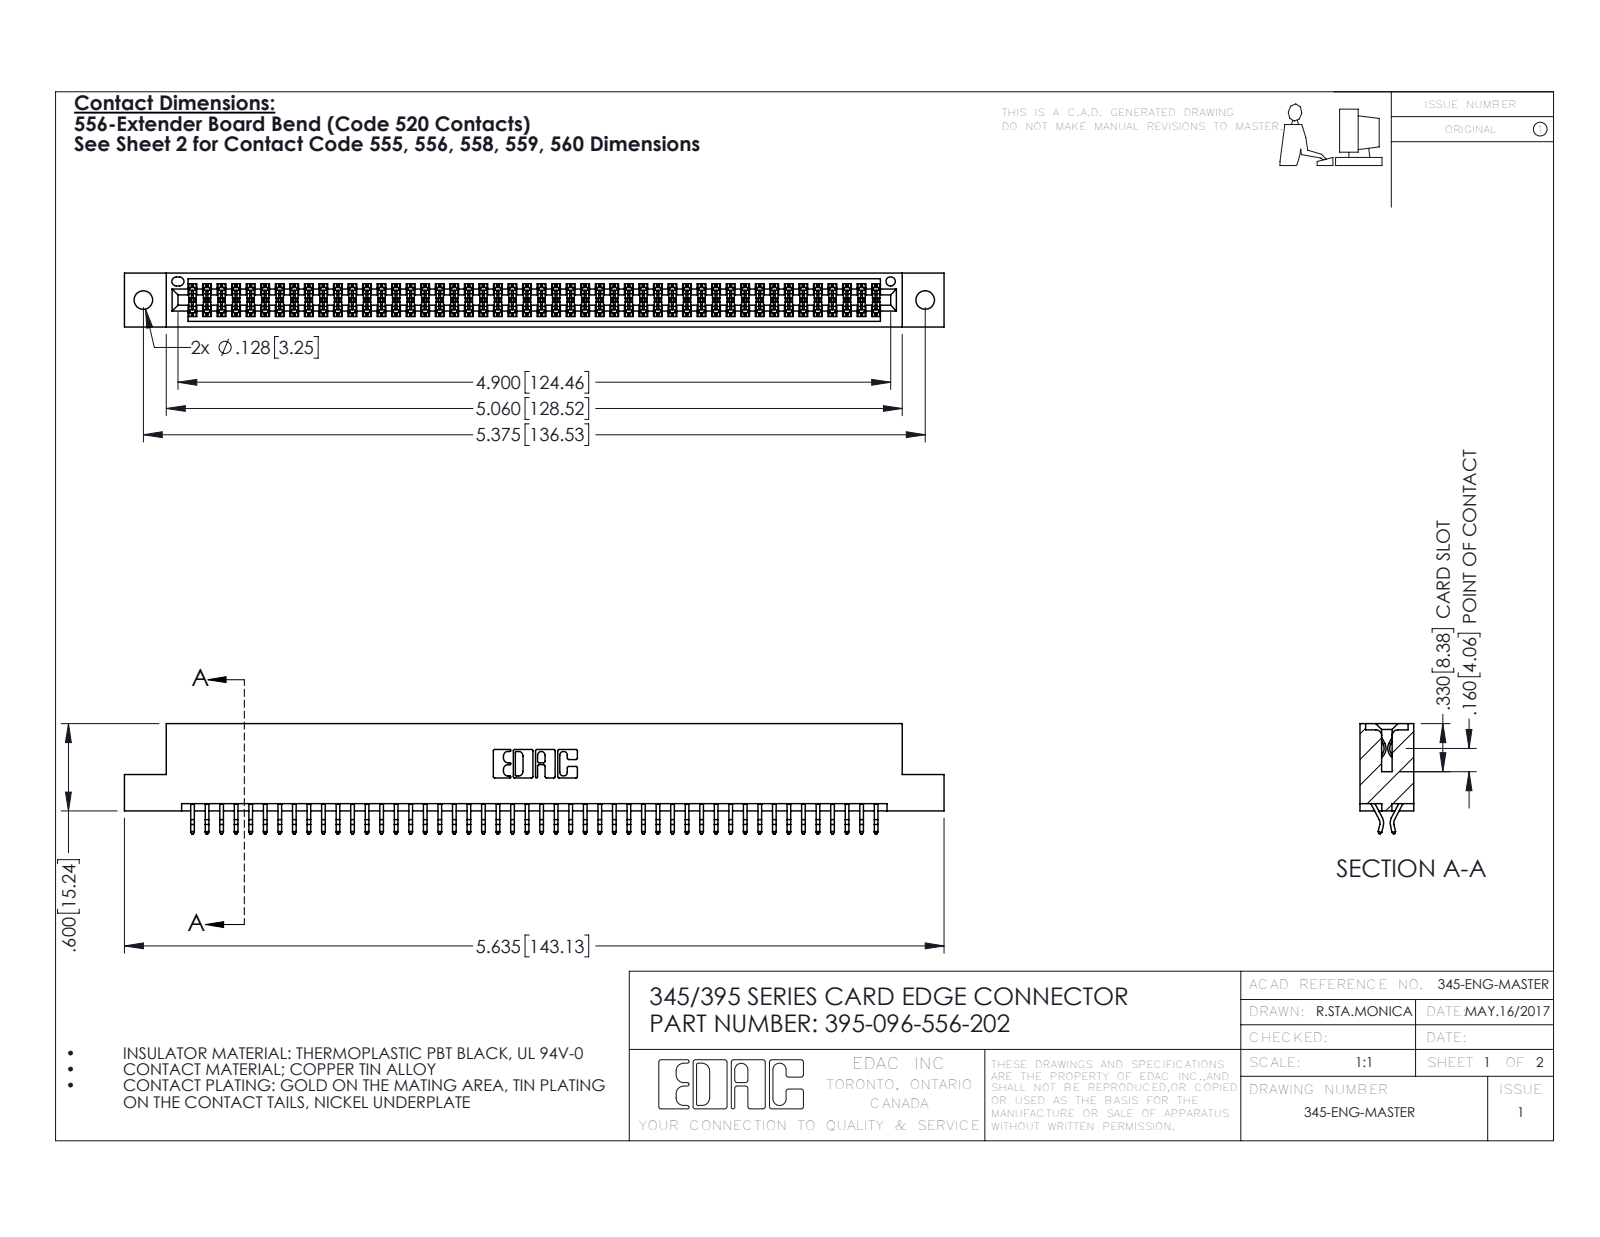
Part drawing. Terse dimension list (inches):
name: 395-096-556-202; 345-292-001_556 Tail; 345 Part_Flush Mounting Lugs - 0.128 Dia
written by: SolidWorks 2016 (CONFIG_CONTROL_DESIGN)
unit: in
bodies: 97 solids, 5502 faces (3632 planar, 1870 cylindrical, 0 other)
size: 5.635 × 0.757 × 0.37
volume: 0.849 in³; area: 31.52 in²
holes: 2× ⌀0.128, 1× ⌀0.064
rounds: 144× R0.006, 22× R0.01, 6× R0.007, 6× R0.031, 3× R0.026, 2× R0.01, 2× R0.014, 2× R0.019
face distances: 0.298, 0.072, 0.37, 0.2, 0.025, 0.098, 0.272, 0.225, 0.175, 0.149
hole spacings: 0.27, 5.139, 5.375
